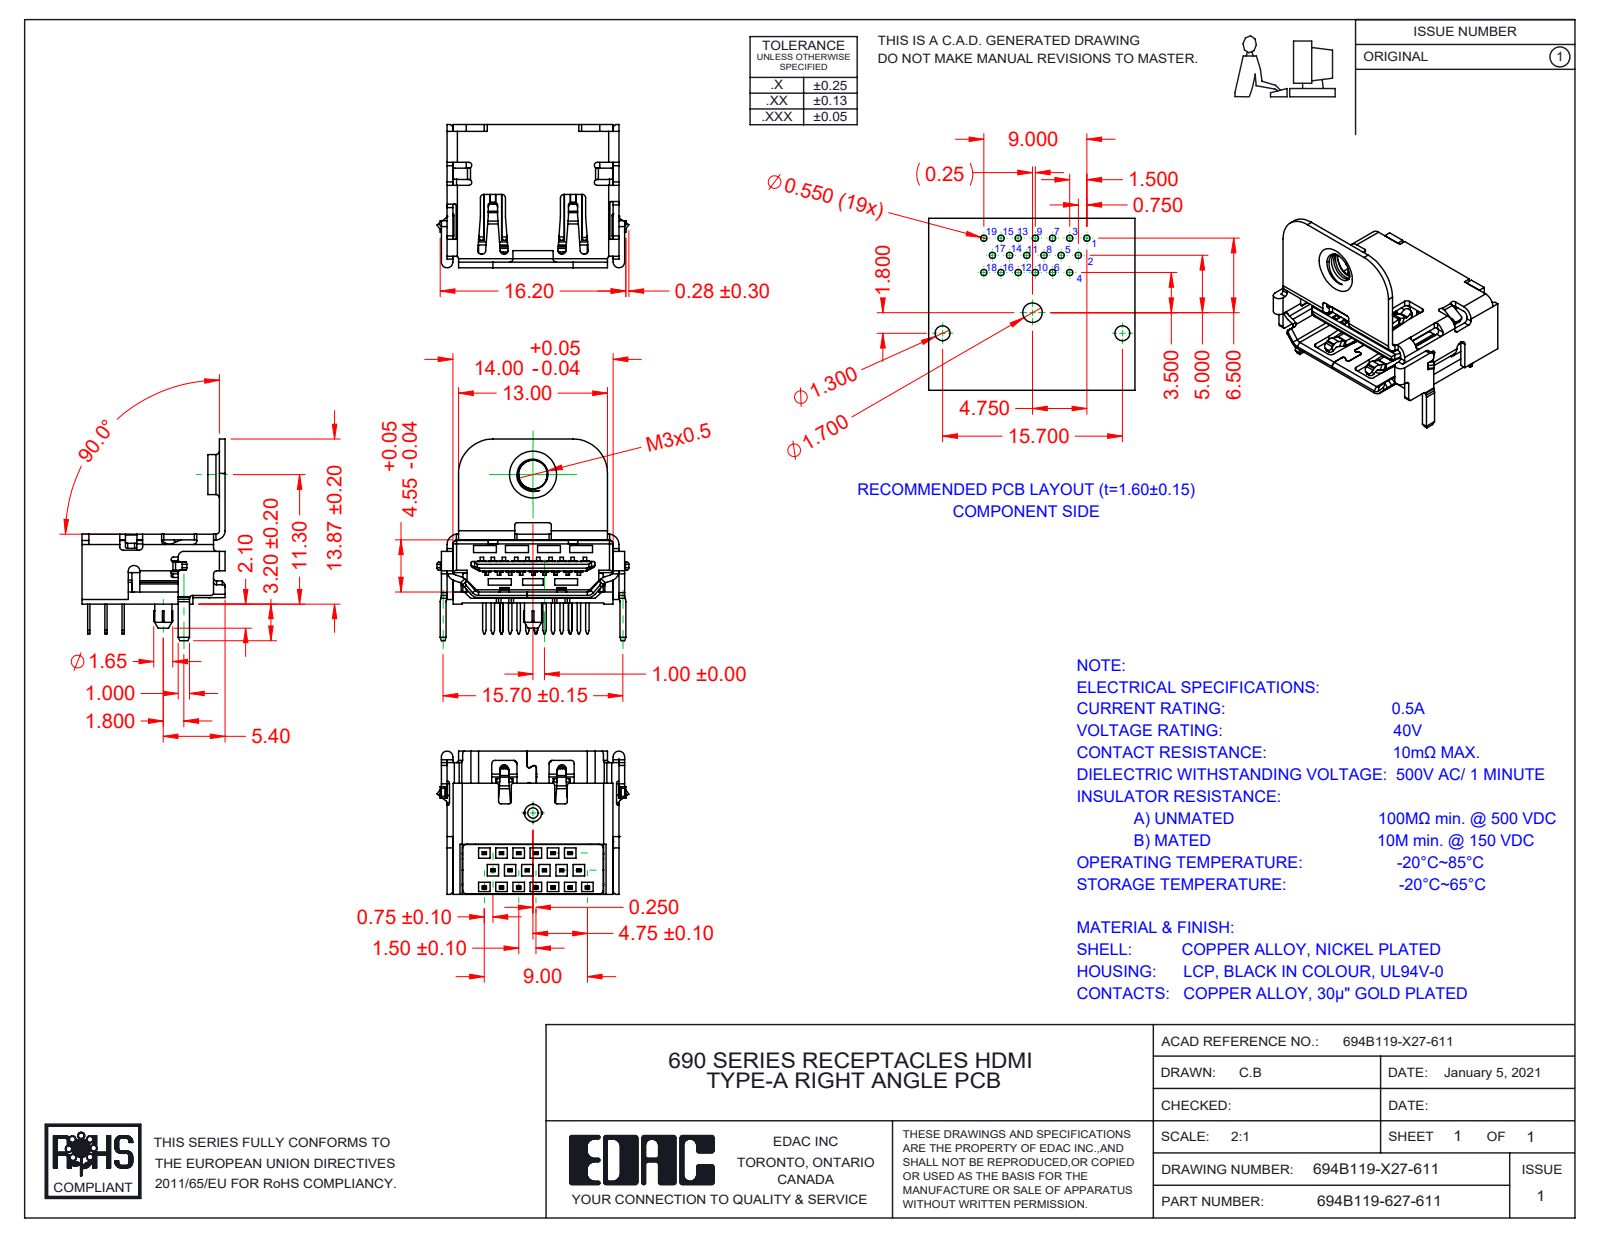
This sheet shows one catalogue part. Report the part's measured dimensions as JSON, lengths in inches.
{"part_name": "Contact 6 694B119-X27-611; Contact 19 694B119-X27-611; Insulator2 694B119-X27-611; Contact 9 694B119-X27-611 (+8 more)", "step_written_by": "SolidWorks 2020 (AUTOMOTIVE_DESIGN)", "units": "inches", "bodies": {"solids": 22, "faces": 2042, "planar": 1664, "cylindrical": 326, "other": 52}, "overall_size": [0.693, 0.659, 0.492], "volume_in3": 0.036, "surface_area_in2": 3.984, "round_holes": [[0.098, 1]], "round_bosses_or_shafts": [[0.138, 1], [0.059, 1]], "partial_cylinders_radius": [[0.008, 45], [0.012, 45], [0.004, 44], [0.01, 16], [0.02, 12], [0.006, 8], [0.016, 7], [0.035, 6]], "face_to_face_distances": [0.02, 0.199, 0.1, 0.02, 0.099, 0.078, 0.022, 0.179, 0.197, 0.12]}
